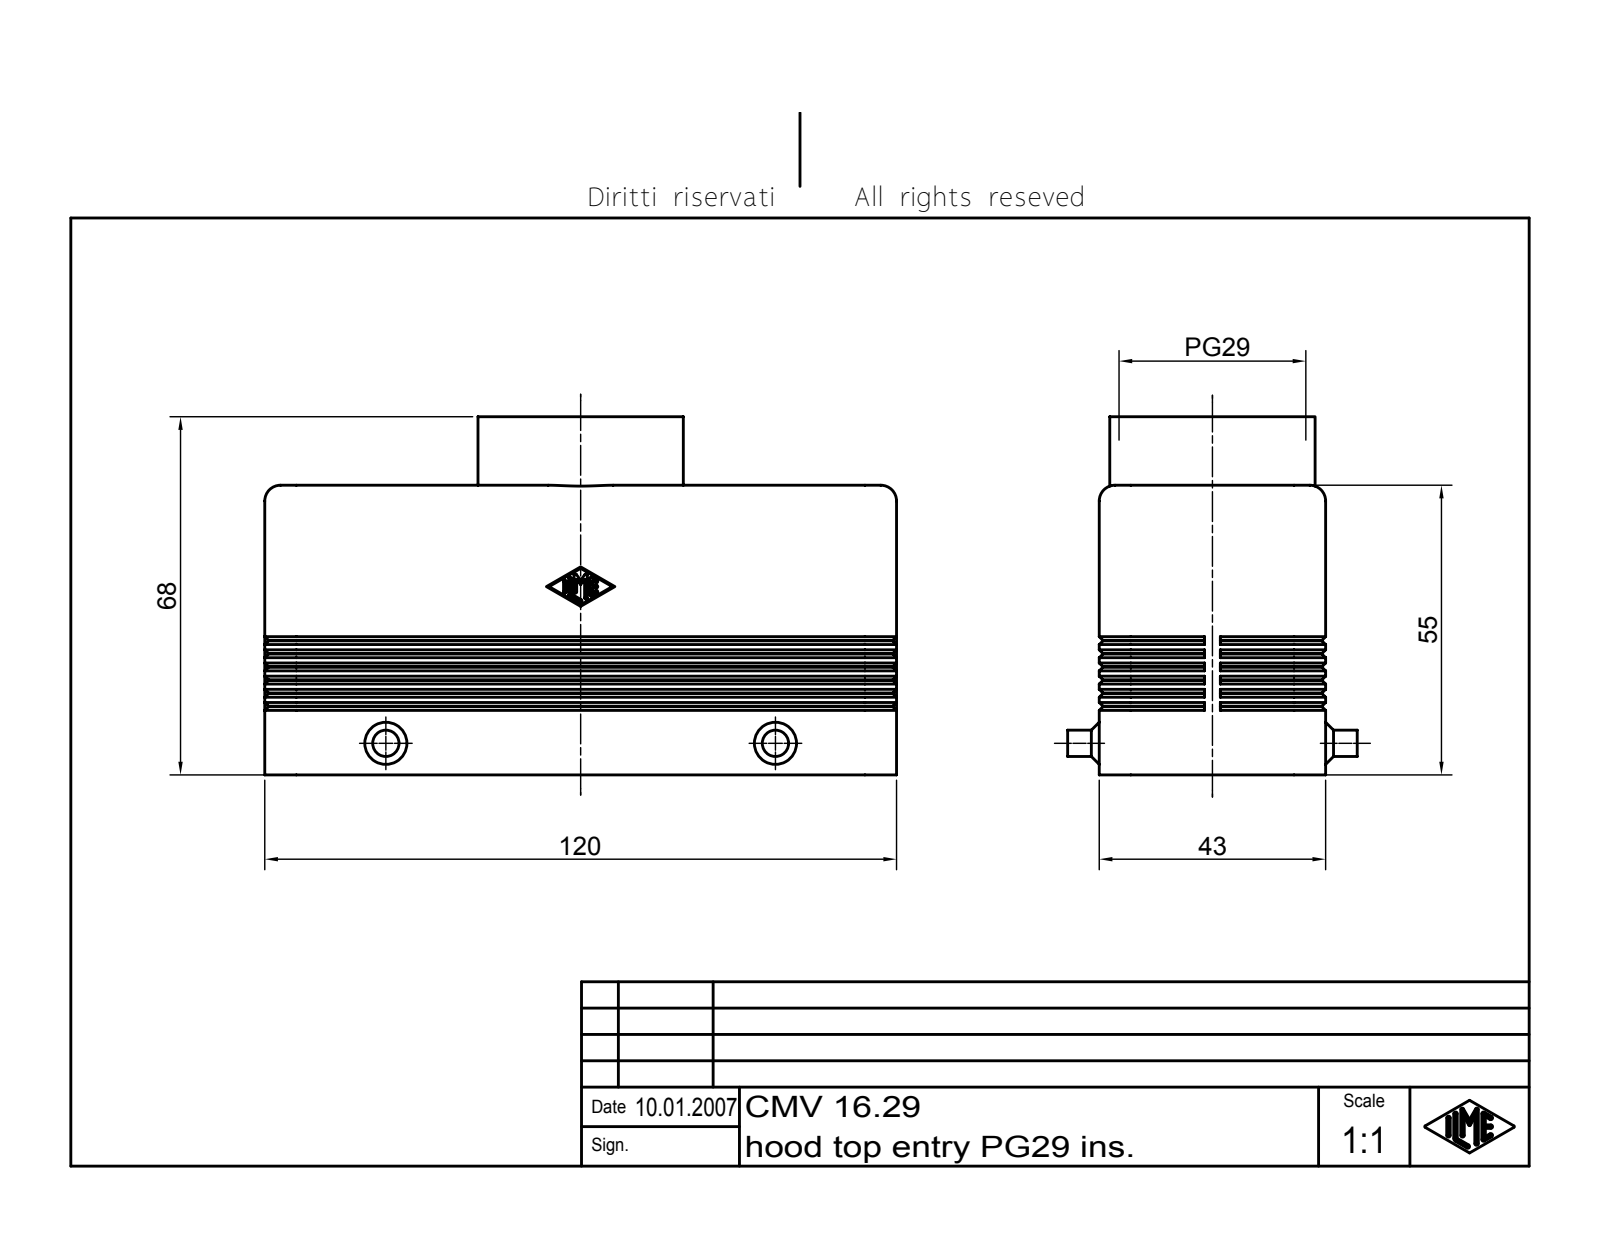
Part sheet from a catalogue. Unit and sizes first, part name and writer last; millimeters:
Units: millimetres
Overall size (bounding box): 120 × 68 × 55
Round holes (diameter × count): ⌀30.32 ×1, ⌀35.48 ×1
Round bosses / shafts (diameter × count): ⌀5 ×2, ⌀39 ×1
Partial cylindrical surfaces — rounded edges, fillets, slot ends (radius × count): R0.25 ×14, R3 ×8, R2 ×4, R6 ×4, R5.3 ×2, R1.5 ×1
Main face-to-face distances: 3, 40, 37, 43, 11.5, 8.5, 1.77, 117, 5.3, 120
Volume: 75 001 mm³ · Surface area: 46 795 mm²
Bodies: 1 solid, 489 faces (182 planar, 113 cylindrical, 194 other)
Part name (STEP PRODUCT): CHV Tüllengehäuse 2 Bügel für einen Einsatz
STEP written by: Autodesk Inventor 7 (AUTOMOTIVE_DESIGN)
